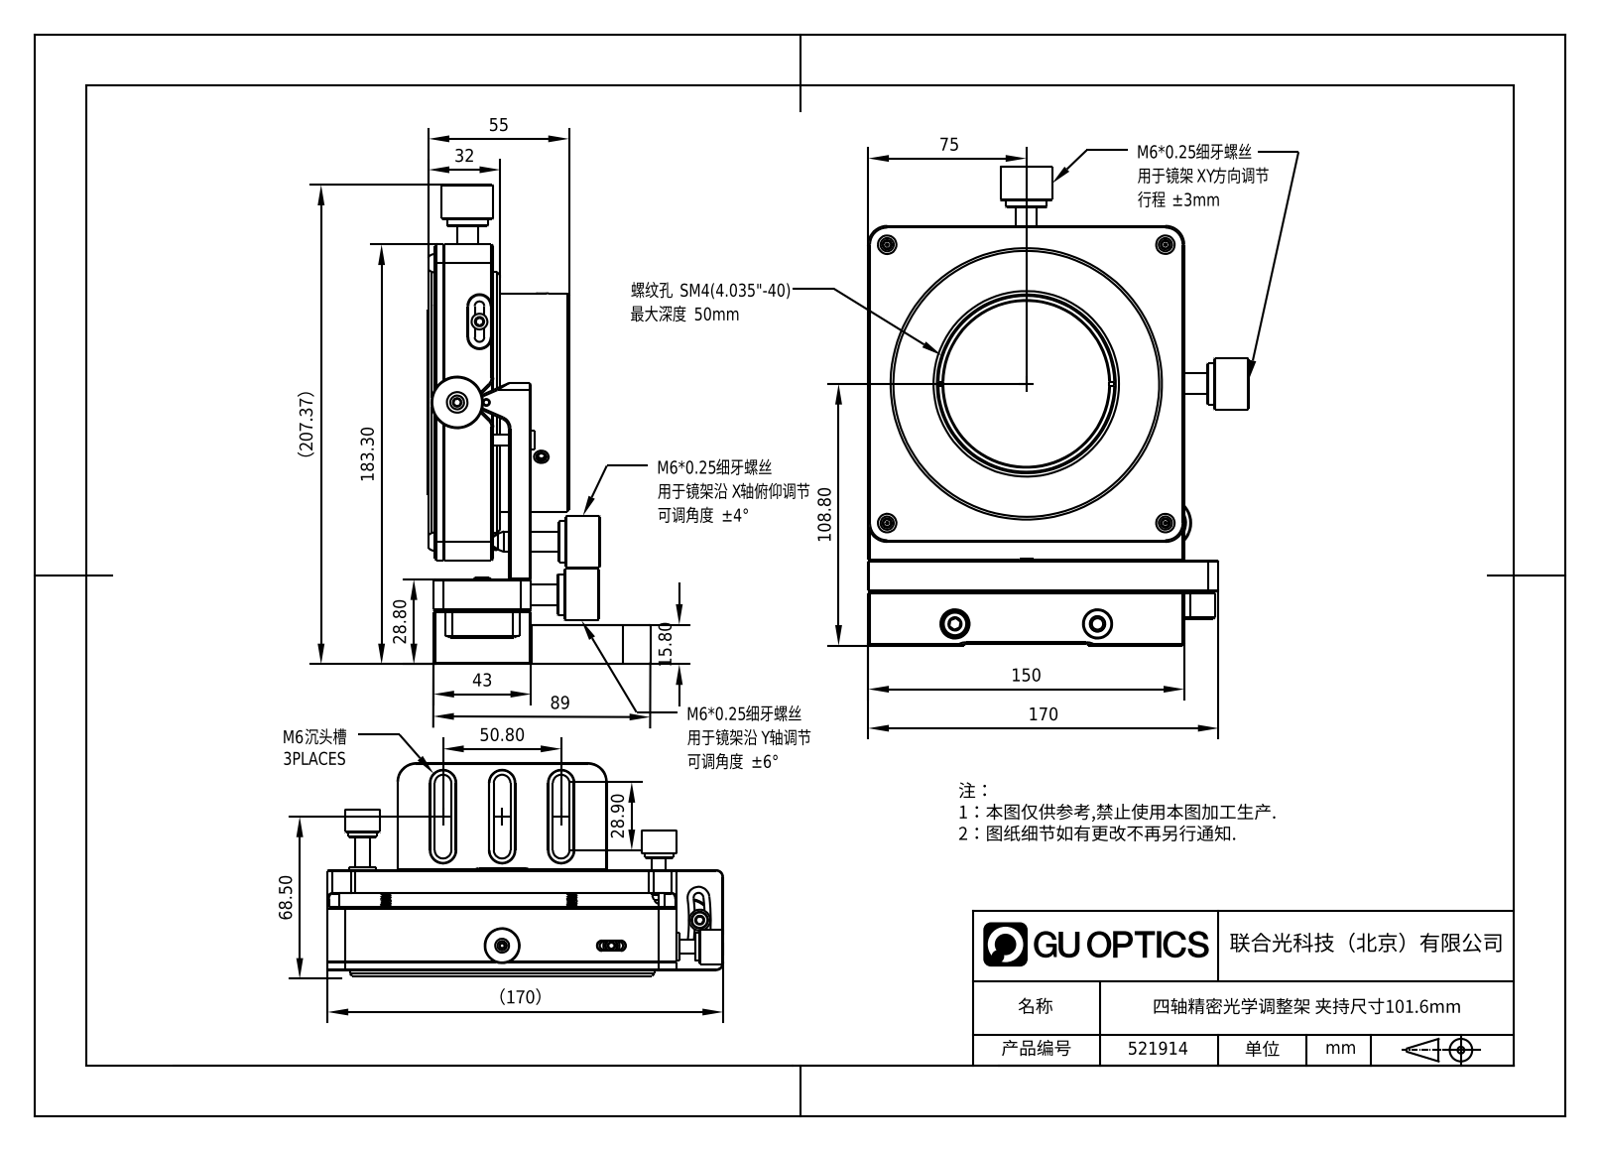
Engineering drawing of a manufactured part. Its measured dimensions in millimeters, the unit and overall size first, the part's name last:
Units: millimetres
Overall size (bounding box): 207.47 × 170.03 × 91.5
Round holes (diameter × count): ⌀3.3 ×9, ⌀6 ×9, ⌀2.5 ×8, ⌀1 ×6, ⌀4 ×5, ⌀4.2 ×5, ⌀3.4 ×4, ⌀5.5 ×3, ⌀9 ×3, ⌀3.99 ×2, ⌀5 ×2, ⌀5.75 ×2
Round bosses / shafts (diameter × count): ⌀4 ×6, ⌀15 ×4, ⌀12 ×4, ⌀11.8 ×3, ⌀9.5 ×3, ⌀8.5 ×3, ⌀3 ×3, ⌀7.2 ×2
Partial cylindrical surfaces — rounded edges, fillets, slot ends (radius × count): R0.8 ×8, R2 ×7, R3 ×7, R3.55 ×6, R5.45 ×6, R2.25 ×4, R5 ×3, R7.5 ×3
Main face-to-face distances: 43, 27, 16, 150, 29.5, 2.5, 6, 10, 45.5, 28.8
Hole centre spacings: 4.75, 20, 31.15, 80, 97.58, 138, 9.5, 60
Volume: 771 694 mm³ · Surface area: 150 029 mm²
Bodies: 24 solids, 1497 faces (549 planar, 386 cylindrical, 562 other)
Part name (STEP PRODUCT): 521914
STEP written by: SolidWorks 2020 (CONFIG_CONTROL_DESIGN)
